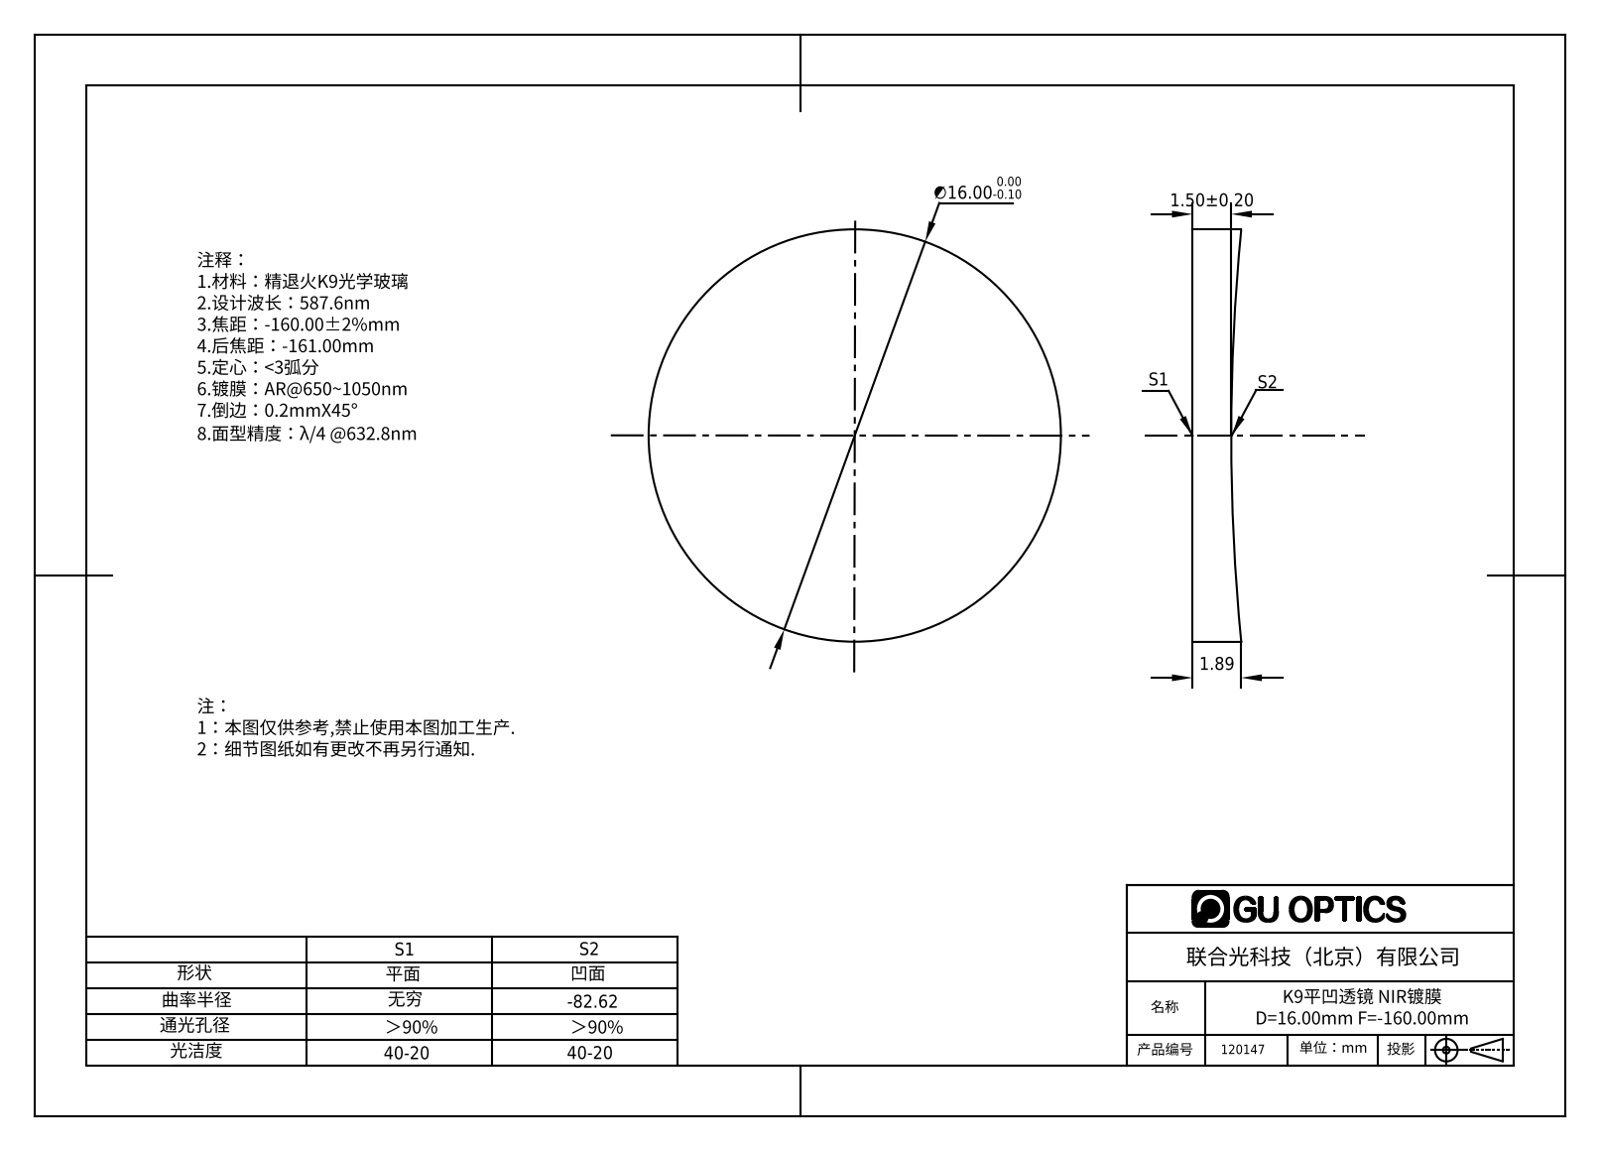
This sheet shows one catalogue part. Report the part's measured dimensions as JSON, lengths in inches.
{"part_name": "120147", "step_written_by": "SolidWorks 2016 (AUTOMOTIVE_DESIGN)", "units": "inches", "bodies": {"solids": 1, "faces": 5, "planar": 1, "cylindrical": 2, "other": 2}, "overall_size": [0.63, 0.63, 0.074], "volume_in3": 0.021, "surface_area_in2": 0.772, "round_bosses_or_shafts": [[0.63, 1]]}
